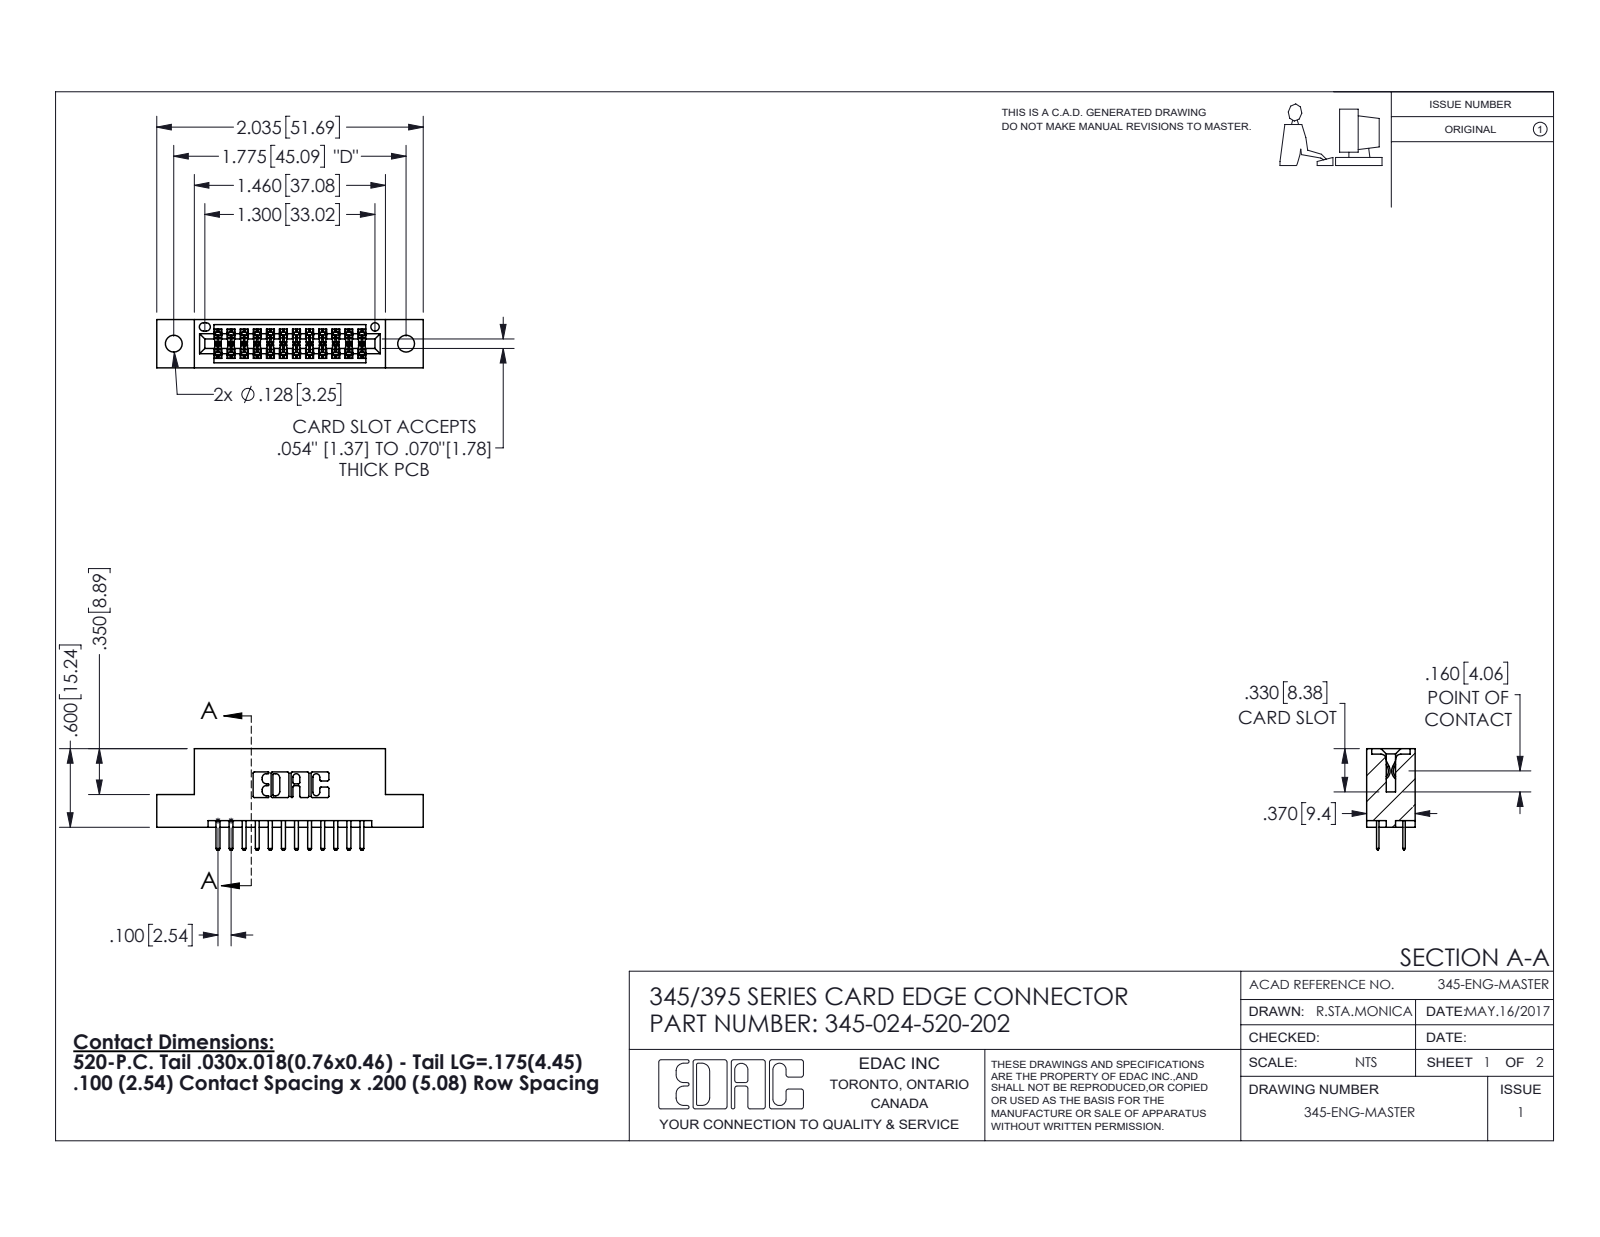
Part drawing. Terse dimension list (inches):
name: 345 Part_Flush Mounting Lugs - 0.128 Dia; 345-024-520-202; 345-292-001_345-293-120
written by: SolidWorks 2016 (CONFIG_CONTROL_DESIGN)
unit: in
bodies: 25 solids, 1422 faces (920 planar, 502 cylindrical, 0 other)
size: 2.035 × 0.775 × 0.37
volume: 0.287 in³; area: 9.4 in²
holes: 2× ⌀0.128, 1× ⌀0.064
rounds: 36× R0.006, 28× R0.01, 22× R0.01, 6× R0.007, 6× R0.031, 3× R0.026, 2× R0.014, 2× R0.019
face distances: 0.2, 0.298, 0.072, 0.37, 0.098, 0.272, 0.025, 0.1, 0.225, 0.6
hole spacings: 0.27, 1.543, 1.775
